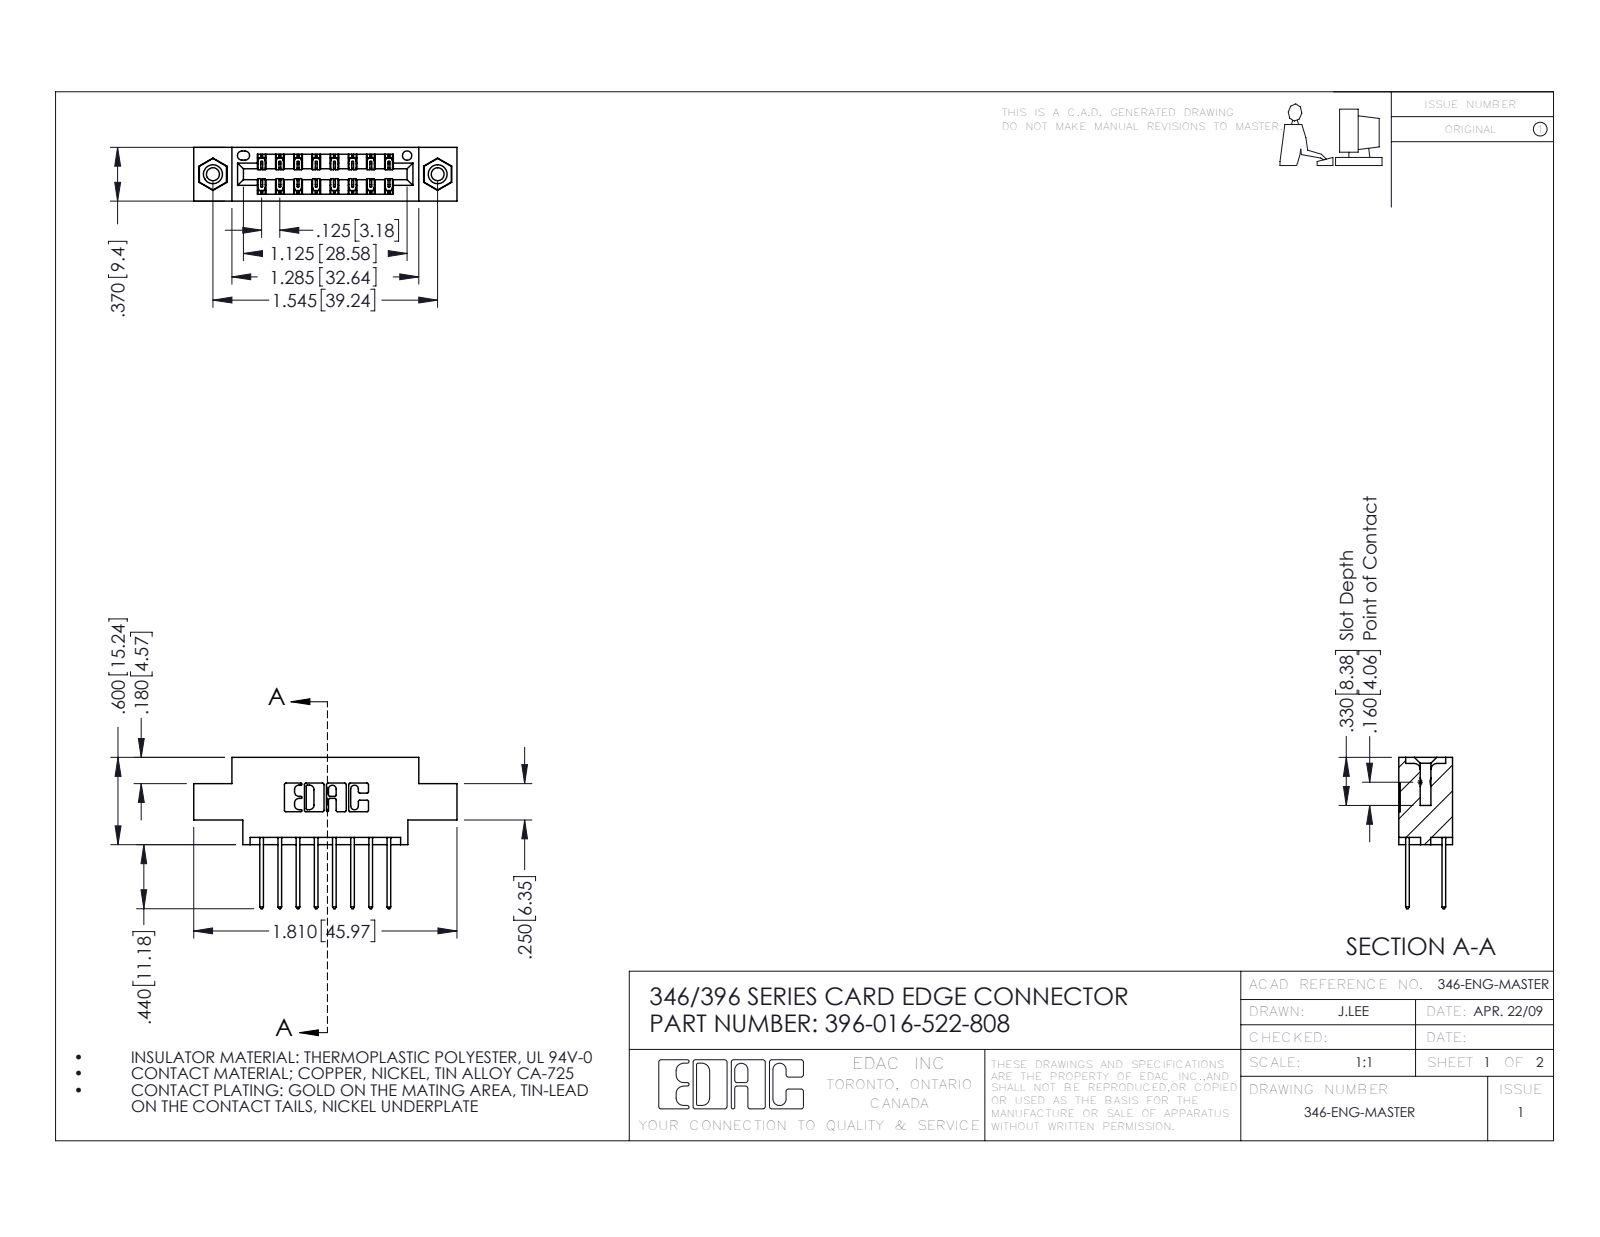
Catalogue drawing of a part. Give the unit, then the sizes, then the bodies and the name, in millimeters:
Units: millimetres
Overall size (bounding box): 46 × 26.4 × 9.4
Round holes (diameter × count): ⌀2.3 ×2, ⌀3.2 ×2, ⌀4 ×2, ⌀1.6 ×1
Round bosses / shafts (diameter × count): ⌀3.9 ×2
Partial cylindrical surfaces — rounded edges, fillets, slot ends (radius × count): R0.2 ×24, R0.3 ×22, R0.3 ×16, R0.2 ×6, R0.8 ×6, R0.7 ×3, R0.4 ×2, R0.6 ×2
Main face-to-face distances: 6.4, 1.2, 8.2, 9.4, 1.8, 7.6, 0.6, 7, 5.6, 3.8
Hole centre spacings: 6.2, 34.1, 39.2
Volume: 4 100 mm³ · Surface area: 5 490 mm²
Bodies: 19 solids, 1018 faces (672 planar, 330 cylindrical, 16 other)
Part name (STEP PRODUCT): 396-016-522-808; 345-292-001_345-293-122; 346 Part_0.170 Offset - 0.156 Dia-TI; 345-250-001_345-250-003-102
STEP written by: SolidWorks 2016 (CONFIG_CONTROL_DESIGN)
